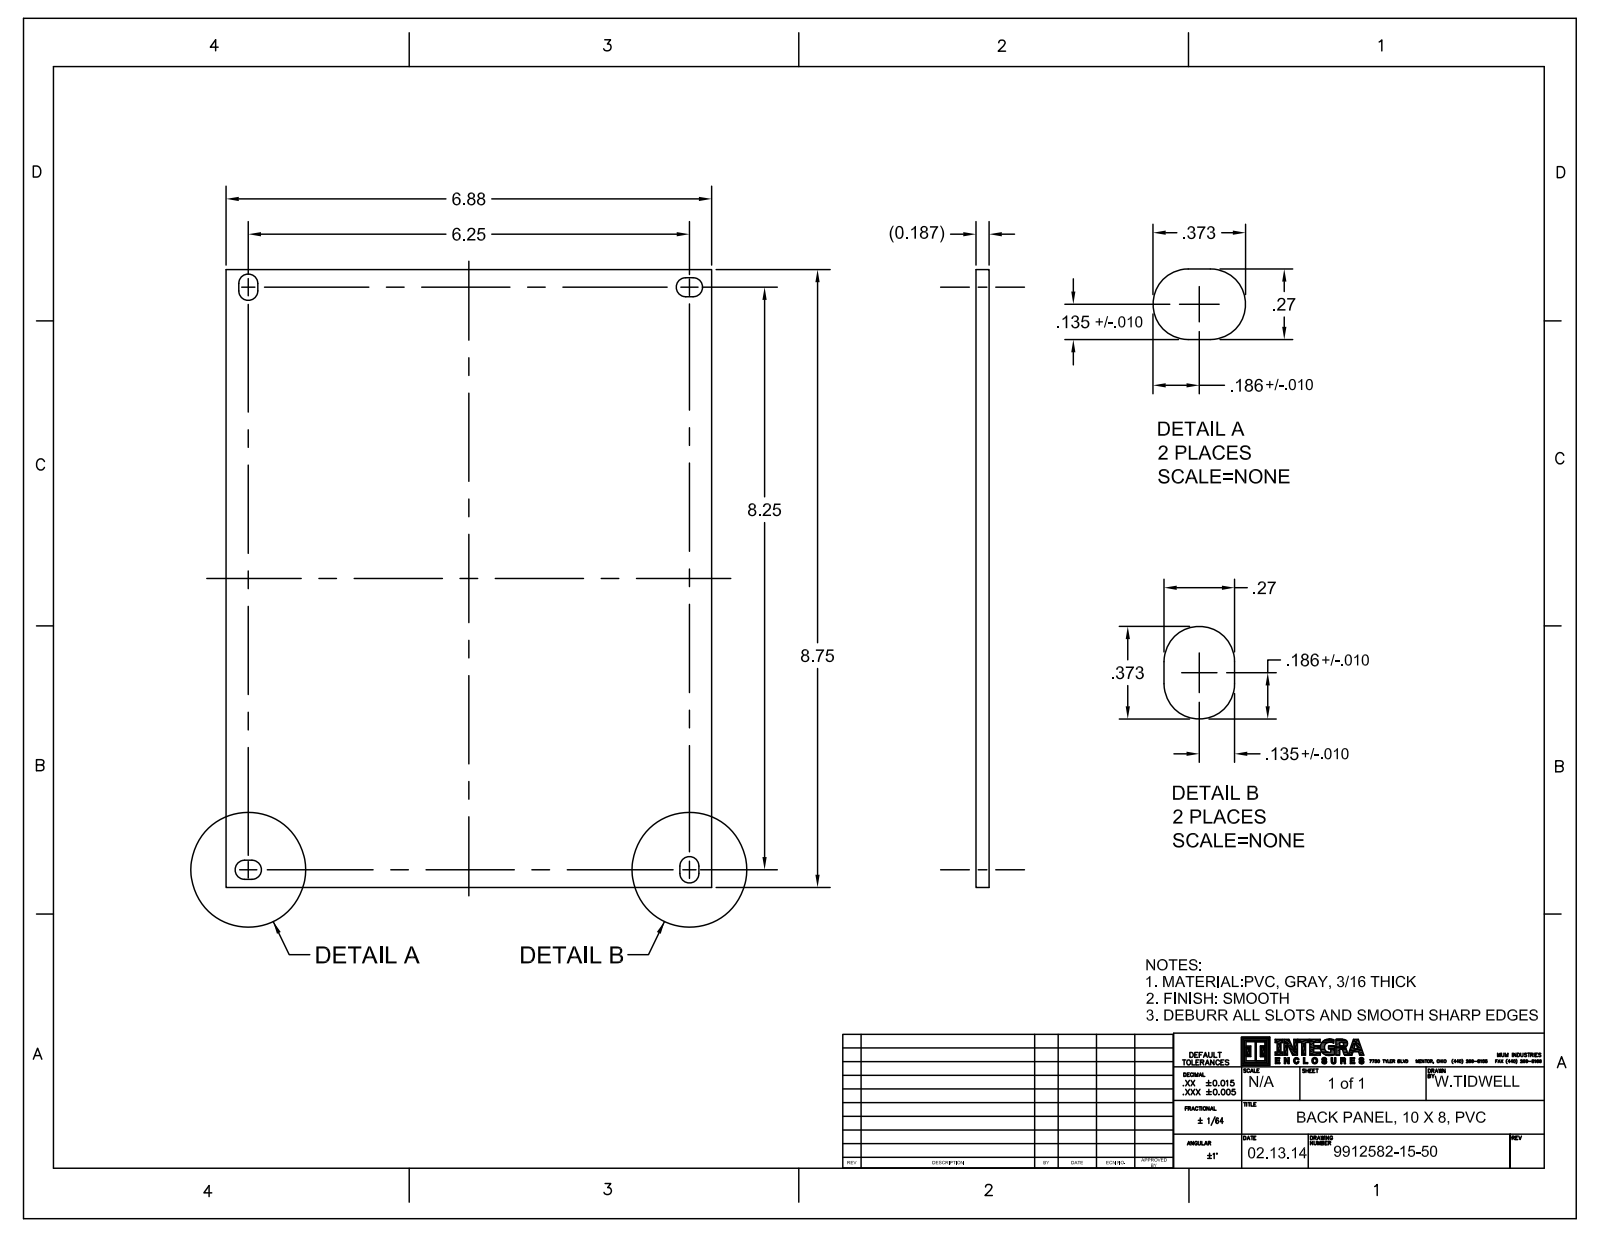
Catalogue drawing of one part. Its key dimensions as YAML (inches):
part_name: "9912582-15-50; 9912596-82-10; PVCBP108-IMP_ASM"
step_written_by: "CREO PARAMETRIC BY PTC INC, 2016050 (CONFIG_CONTROL_DESIGN)"
units: inches
bodies: {solids: 5, faces: 506, planar: 114, cylindrical: 204, other: 188}
overall_size: [8.75, 6.88, 0.615]
volume: 11.29
surface_area: 128.8
round_bosses_or_shafts:
  - {diameter: 0.322, count: 4}
  - {diameter: 0.164, count: 4}
  - {diameter: 0.119, count: 4}
partial_cylinders:
  - {radius: 0.125, count: 8}
face_to_face_distances: [0.187, 6.88, 8.75, 0.25, 0.125, 0.375, 8.375, 8.625, 8.25, 0.19]
